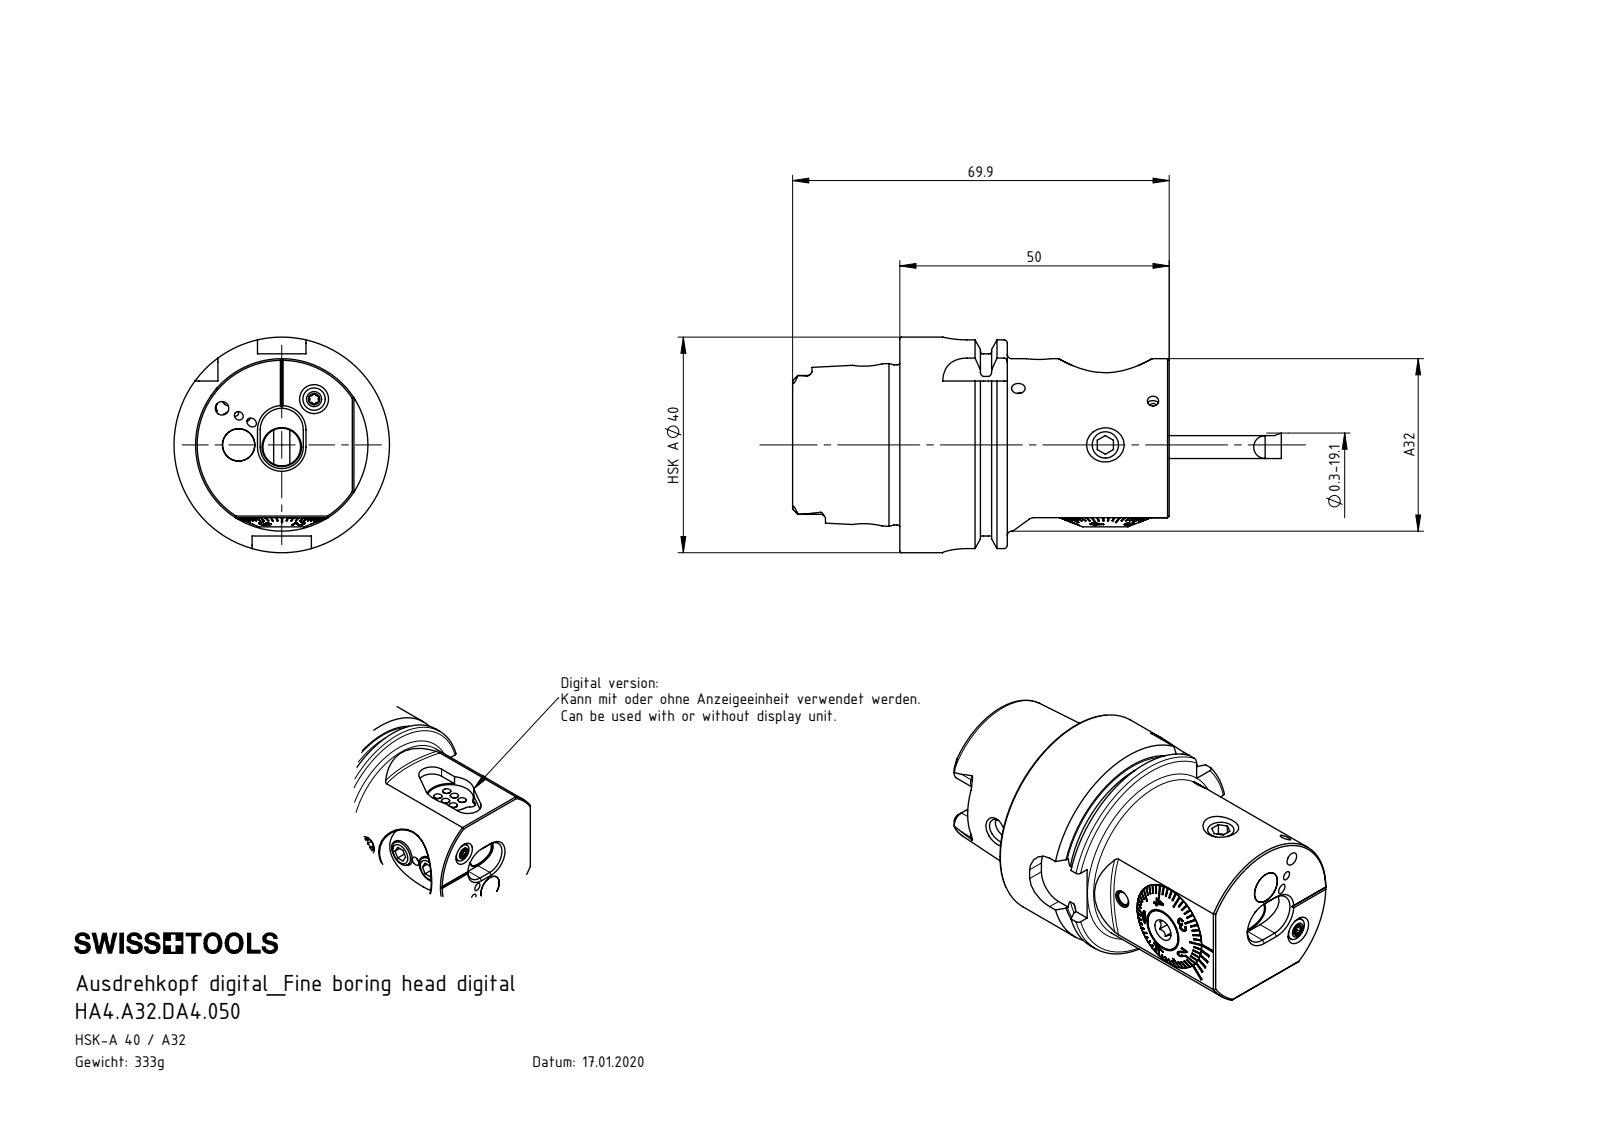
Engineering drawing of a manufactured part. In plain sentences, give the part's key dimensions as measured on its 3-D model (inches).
The part is named "Fxx-MAB.xxx.xxx_A_F32x1.3; A32-BG1.DA3.017_A; F32-BG2.017.004_A; HA4-A32.DA3.050_A (+8 more)". Its 3-D file was written by "SolidWorks 2017 (CONFIG_CONTROL_DESIGN)". It is 17 solids with 799 faces: 456 planar, 132 cylindrical and 211 other. Overall it measures 2.752 by 1.575 by 1.575 inches. Its volume is 2.668 cubic inches and its surface area 33.4 square inches. Round holes: 4 of diameter 0.197, 3 of diameter 0.098, 2 of diameter 0.059, 2 of diameter 0.13, 1 of diameter 0.039, 1 of diameter 0.079, 1 of diameter 0.083, 1 of diameter 0.114, 1 of diameter 0.118, 1 of diameter 0.165, 1 of diameter 0.181, 1 of diameter 0.236. Round bosses or shafts: 6 of diameter 0.075, 3 of diameter 0.236, 1 of diameter 1.575, 1 of diameter 1.368, 1 of diameter 1.26, 1 of diameter 1.17, 1 of diameter 0.669, 1 of diameter 0.669. Partial cylindrical surfaces (rounded edges, fillets, slot ends): 6 of radius 0.008, 6 of radius 0.035, 6 of radius 0.055, 5 of radius 0.014, 4 of radius 0.074, 4 of radius 0.177, 3 of radius 0.043, 3 of radius 0.047. The main face-to-face distances are 1.969, 0.177, 0.059, 0.785, 1.183, 0.266, 0.146, 0.031, 0.313, 0.472. The hole center spacings are 0.177, 0.016, 0.044, 0.311, 0.315, 0.315, 0.354, 0.409.
